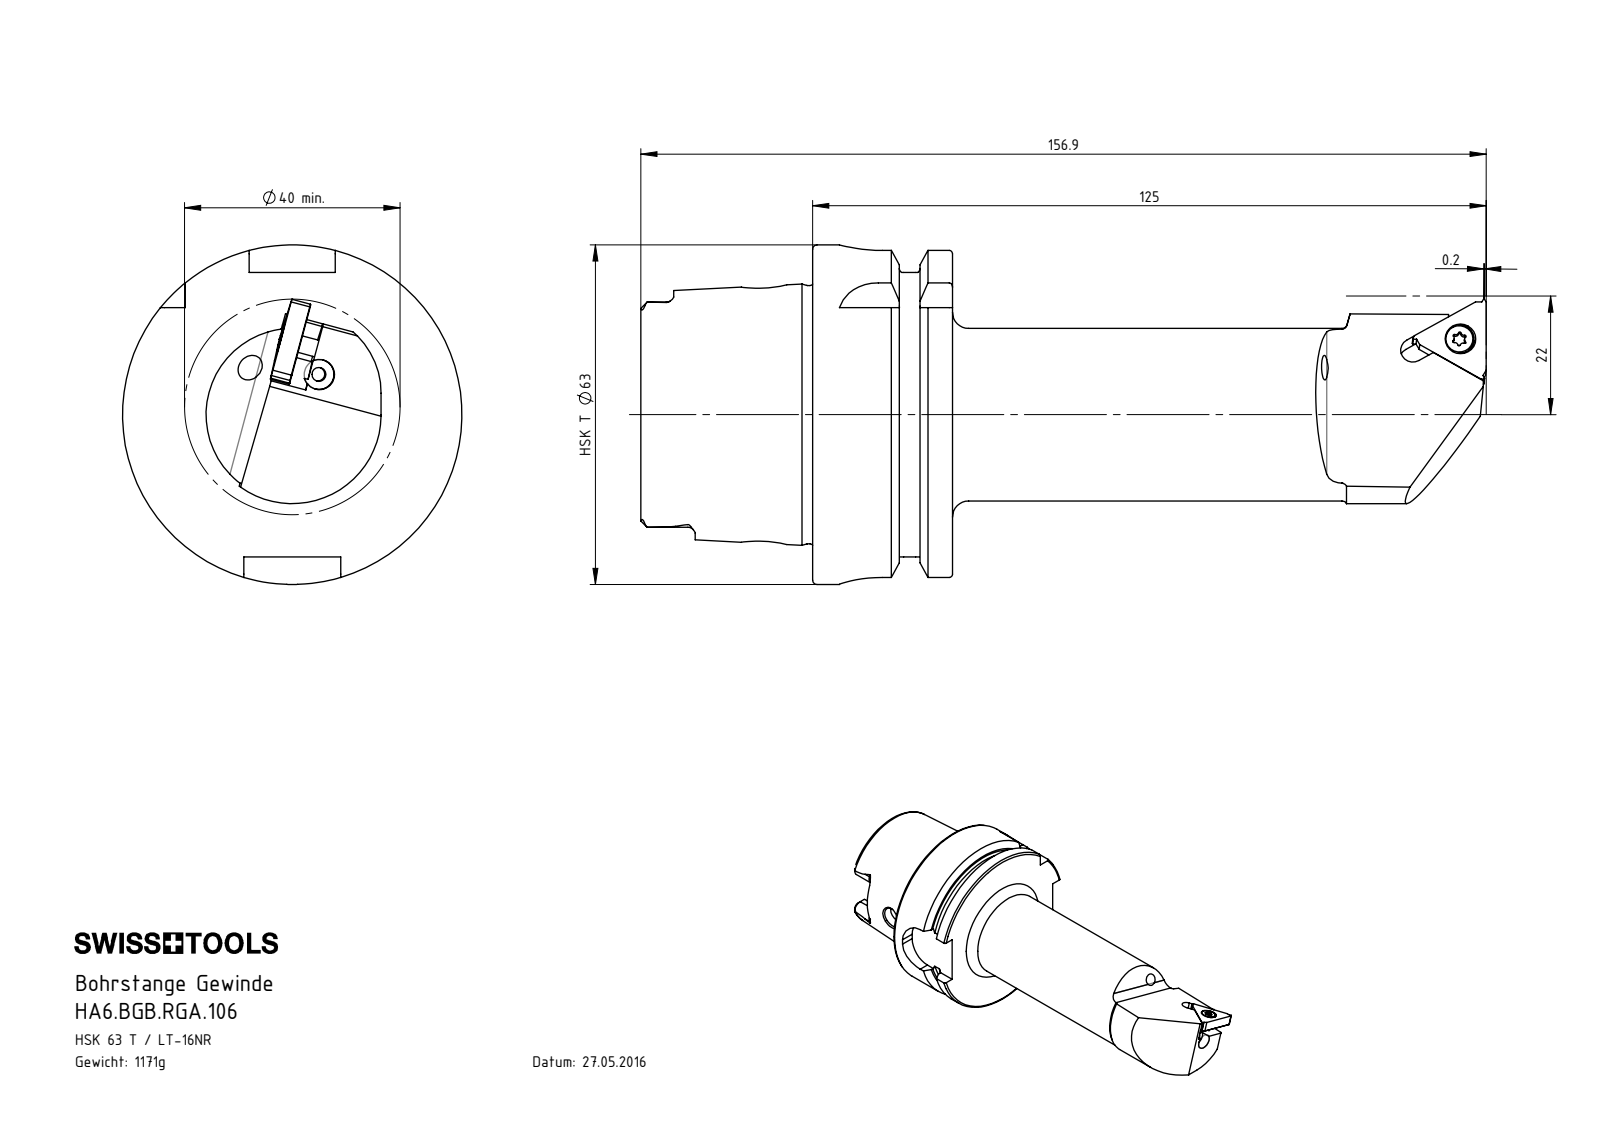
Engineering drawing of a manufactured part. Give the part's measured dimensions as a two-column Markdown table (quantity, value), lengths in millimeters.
| quantity | value |
| --- | --- |
| part name | HA6-BGB.RGA.125; WGB-ER3.001.007_A; LT16EL; WGB-ER2.101.003_A (+2 more) |
| STEP written by | SolidWorks 2012 (AUTOMOTIVE_DESIGN) |
| units | millimeters |
| bodies | 5 solids, 334 faces (113 planar, 115 cylindrical, 106 other) |
| overall size | 156.9 × 63 × 63 |
| volume | 149 312 mm³ |
| surface area | 34 885 mm² |
| round holes (diameter × count) | 2.58 × 2, 4.2 × 2, 4 × 1, 4.03 × 1, 5 × 1, 7.5 × 1, 8.4 × 1, 10 × 1, 17 × 1, 19 × 1, 34 × 1, 40 × 1 |
| round bosses / shafts (diameter × count) | 3.18 × 2, 63 × 1, 54.95 × 1, 47.94 × 1, 32 × 1, 5.5 × 1, 5.4 × 1, 2.78 × 1 |
| partial cylindrical surfaces (radius × count) | 0.23 × 12, 0.57 × 12, 1.4 × 6, 2.88 × 4, 8 × 4, 0.1 × 2, 0.25 × 1, 0.3 × 1 |
| main face-to-face distances | 25.95, 16, 9.95, 31.9, 41.85, 57.85, 52.8, 21.8, 11.85, 53.7 |
| hole center spacings | 467.88, 467.93 |
